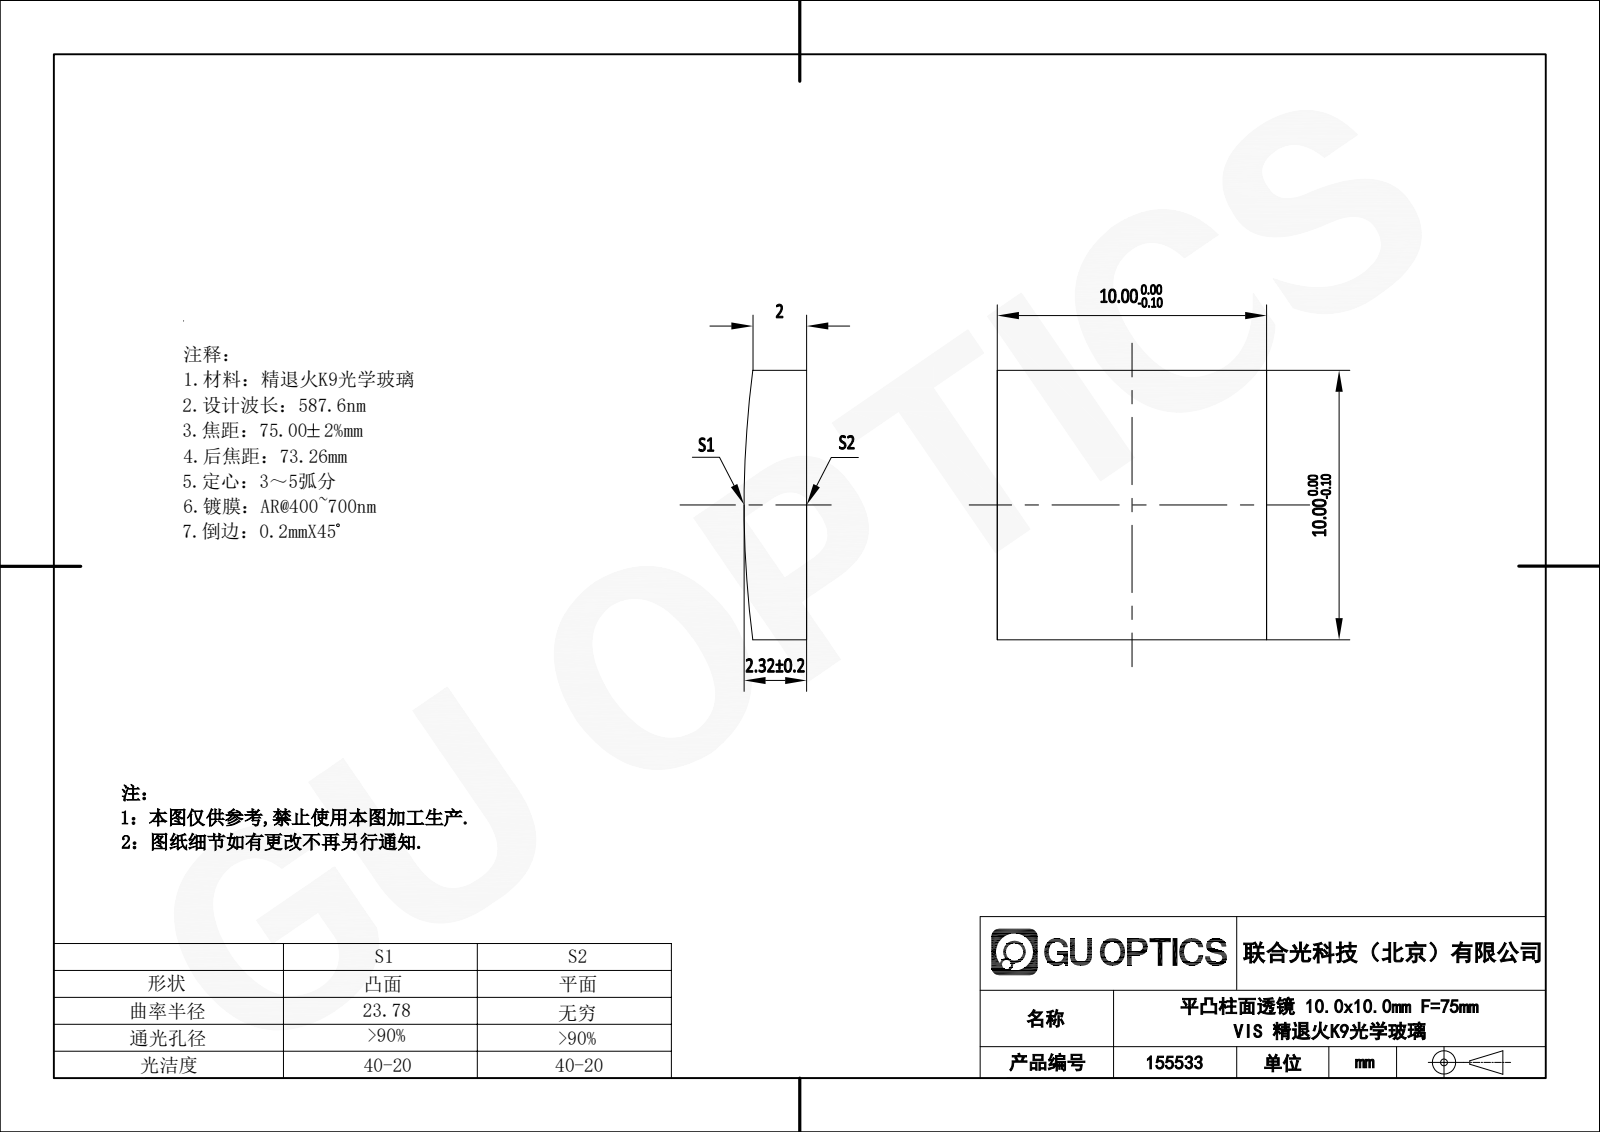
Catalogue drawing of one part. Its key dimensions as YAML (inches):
part_name: "155521"
step_written_by: "SolidWorks 2020 (CONFIG_CONTROL_DESIGN)"
units: inches
bodies: {solids: 1, faces: 7, planar: 5, cylindrical: 2, other: 0}
overall_size: [0.394, 0.394, 0.091]
volume: 0.014
surface_area: 0.442
partial_cylinders:
  - {radius: 1.527, count: 1}
face_to_face_distances: [0.394]
